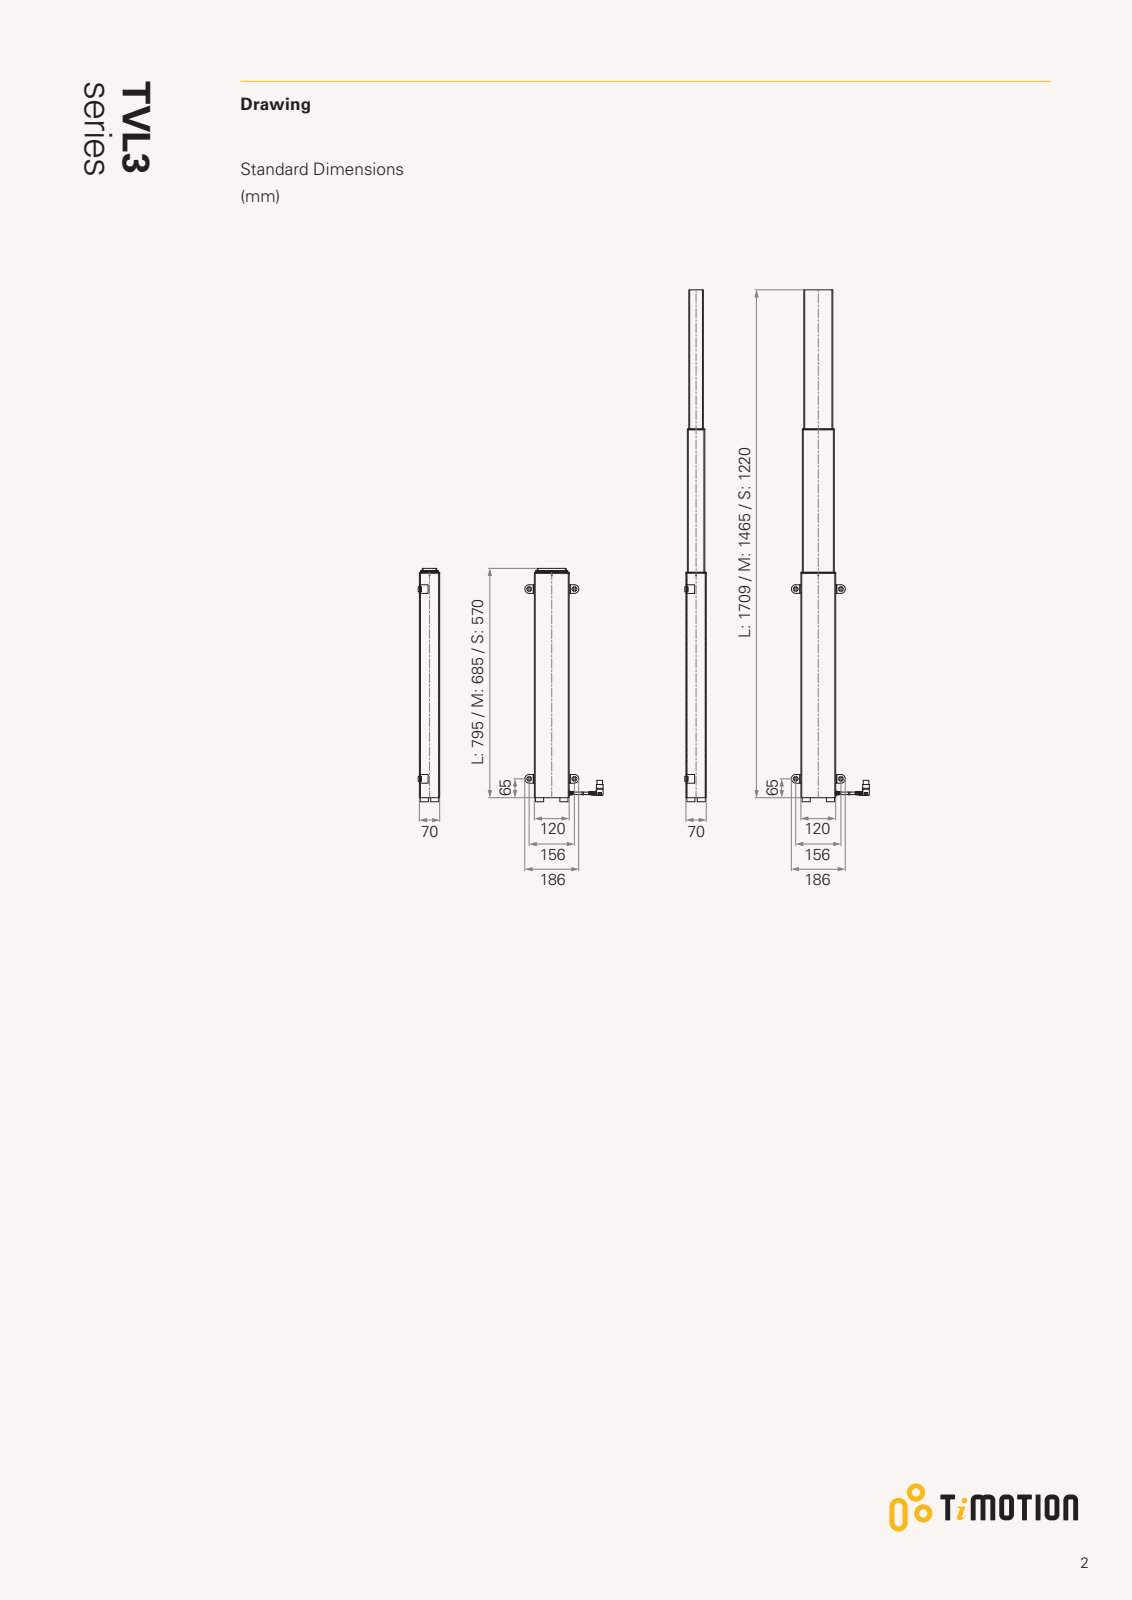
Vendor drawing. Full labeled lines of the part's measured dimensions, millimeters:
Part name (STEP PRODUCT): TVL3-S3
STEP written by: SolidWorks 2010 (CONFIG_CONTROL_DESIGN)
Units: millimetres
Bodies: 0 solids, 511 faces (197 planar, 233 cylindrical, 81 other)
Overall size (bounding box): 620.5 × 550 × 101.5
Round holes (diameter × count): ⌀9.5 ×26, ⌀5 ×4, ⌀6.4 ×4, ⌀8.5 ×4, ⌀13 ×4, ⌀3.2 ×3, ⌀4 ×1, ⌀4.2 ×1
Round bosses / shafts (diameter × count): ⌀28 ×4, ⌀8.4 ×4, ⌀5 ×4, ⌀18 ×3, ⌀8 ×2, ⌀14 ×1, ⌀10 ×1, ⌀6 ×1
Partial cylindrical surfaces — rounded edges, fillets, slot ends (radius × count): R3 ×14, R1 ×10, R5 ×8, R0.5 ×6, R4 ×6, R0.3 ×5, R2.5 ×4, R4.75 ×4
Main face-to-face distances: 5, 80.5, 75.5, 10, 3, 110, 85.5, 8, 16, 15.5
Hole centre spacings: 100, 20, 101.98, 40, 107.7, 60, 80, 116.62
